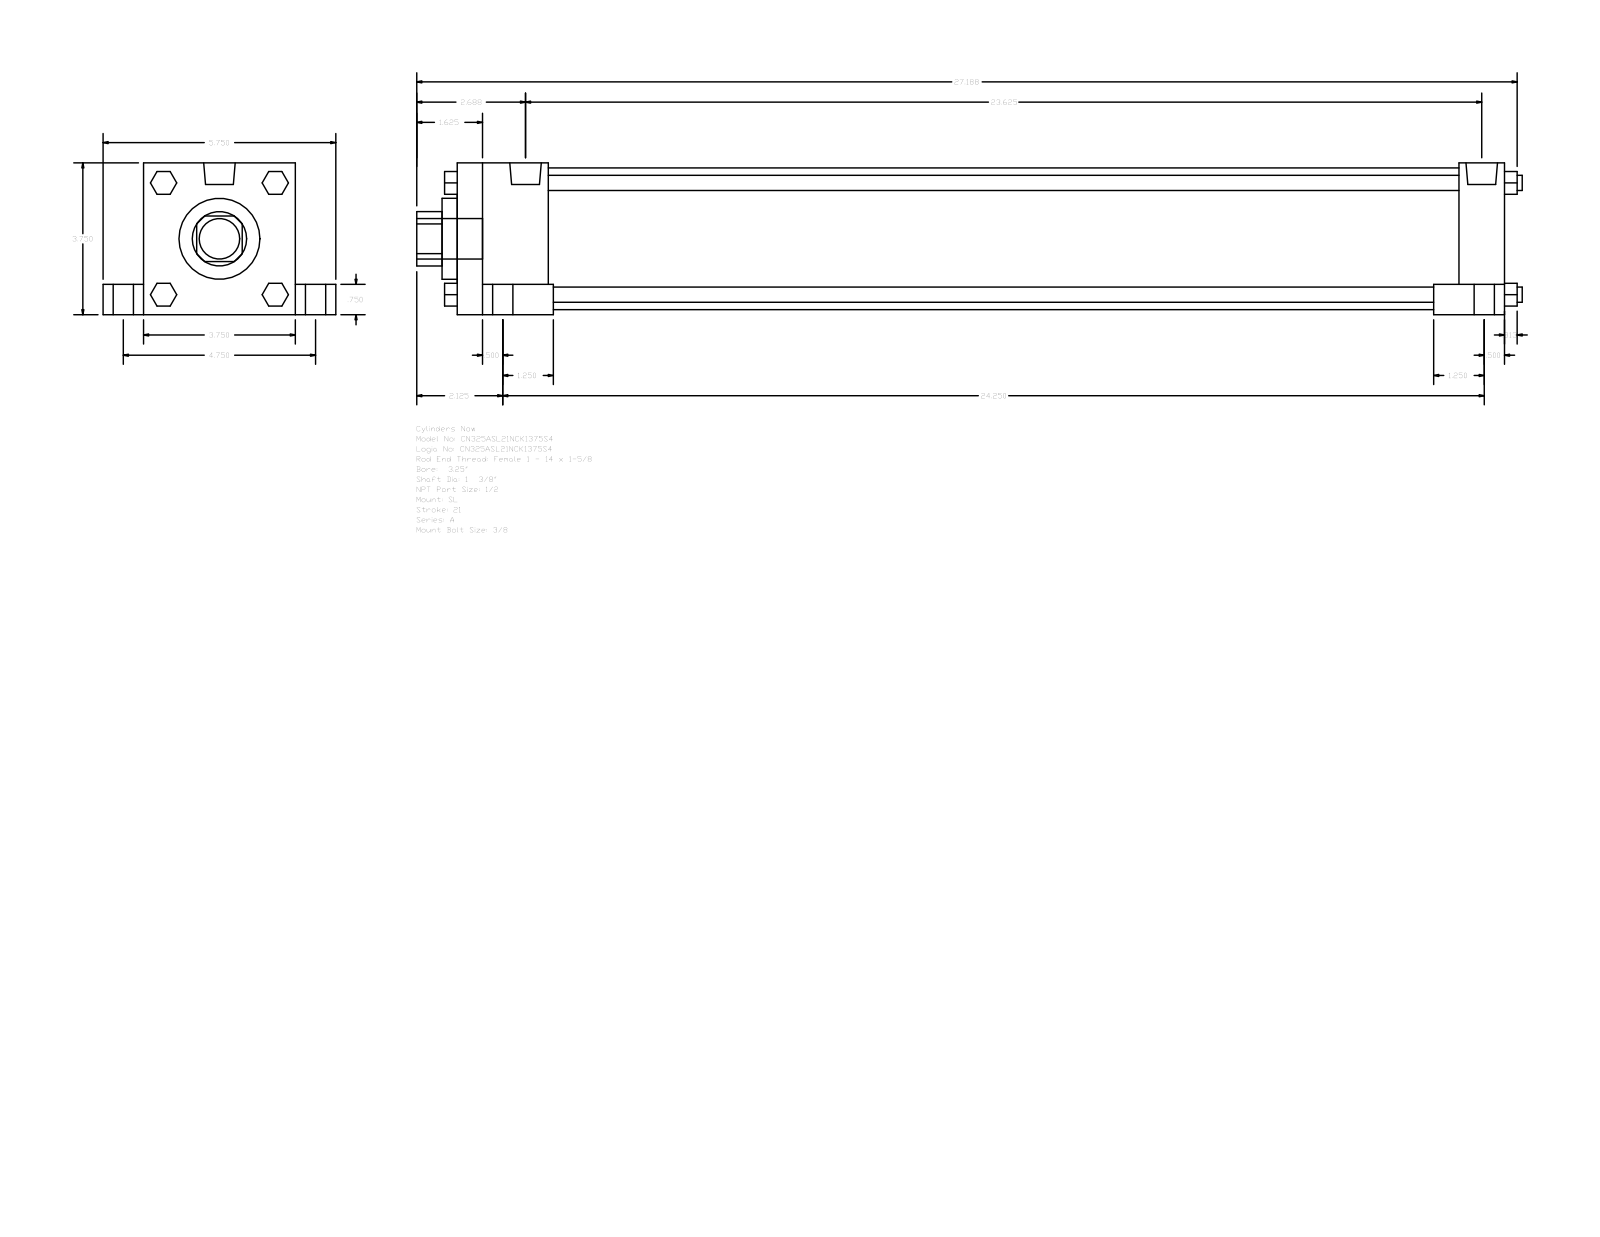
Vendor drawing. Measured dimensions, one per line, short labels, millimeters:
name: A_SL__0325_1.375
written by: GSSL Pune (CONFIG_CONTROL_DESIGN)
unit: mm
bodies: 0 solids, 150 faces (114 planar, 36 cylindrical, 0 other)
size: 693.74 × 146.05 × 95.25
holes: 1× ⌀34.92, 1× ⌀50.8, 1× ⌀88.9
bosses: 4× ⌀19.05, 4× ⌀12.7, 4× ⌀9.53, 4× ⌀8.73, 2× ⌀19.77, 1× ⌀25.4
rounds: 1× R17.06
face distances: 95.24, 657.22, 25.41, 120.65, 19.05, 76.19, 28.57, 57.15, 628.65, 571.5
